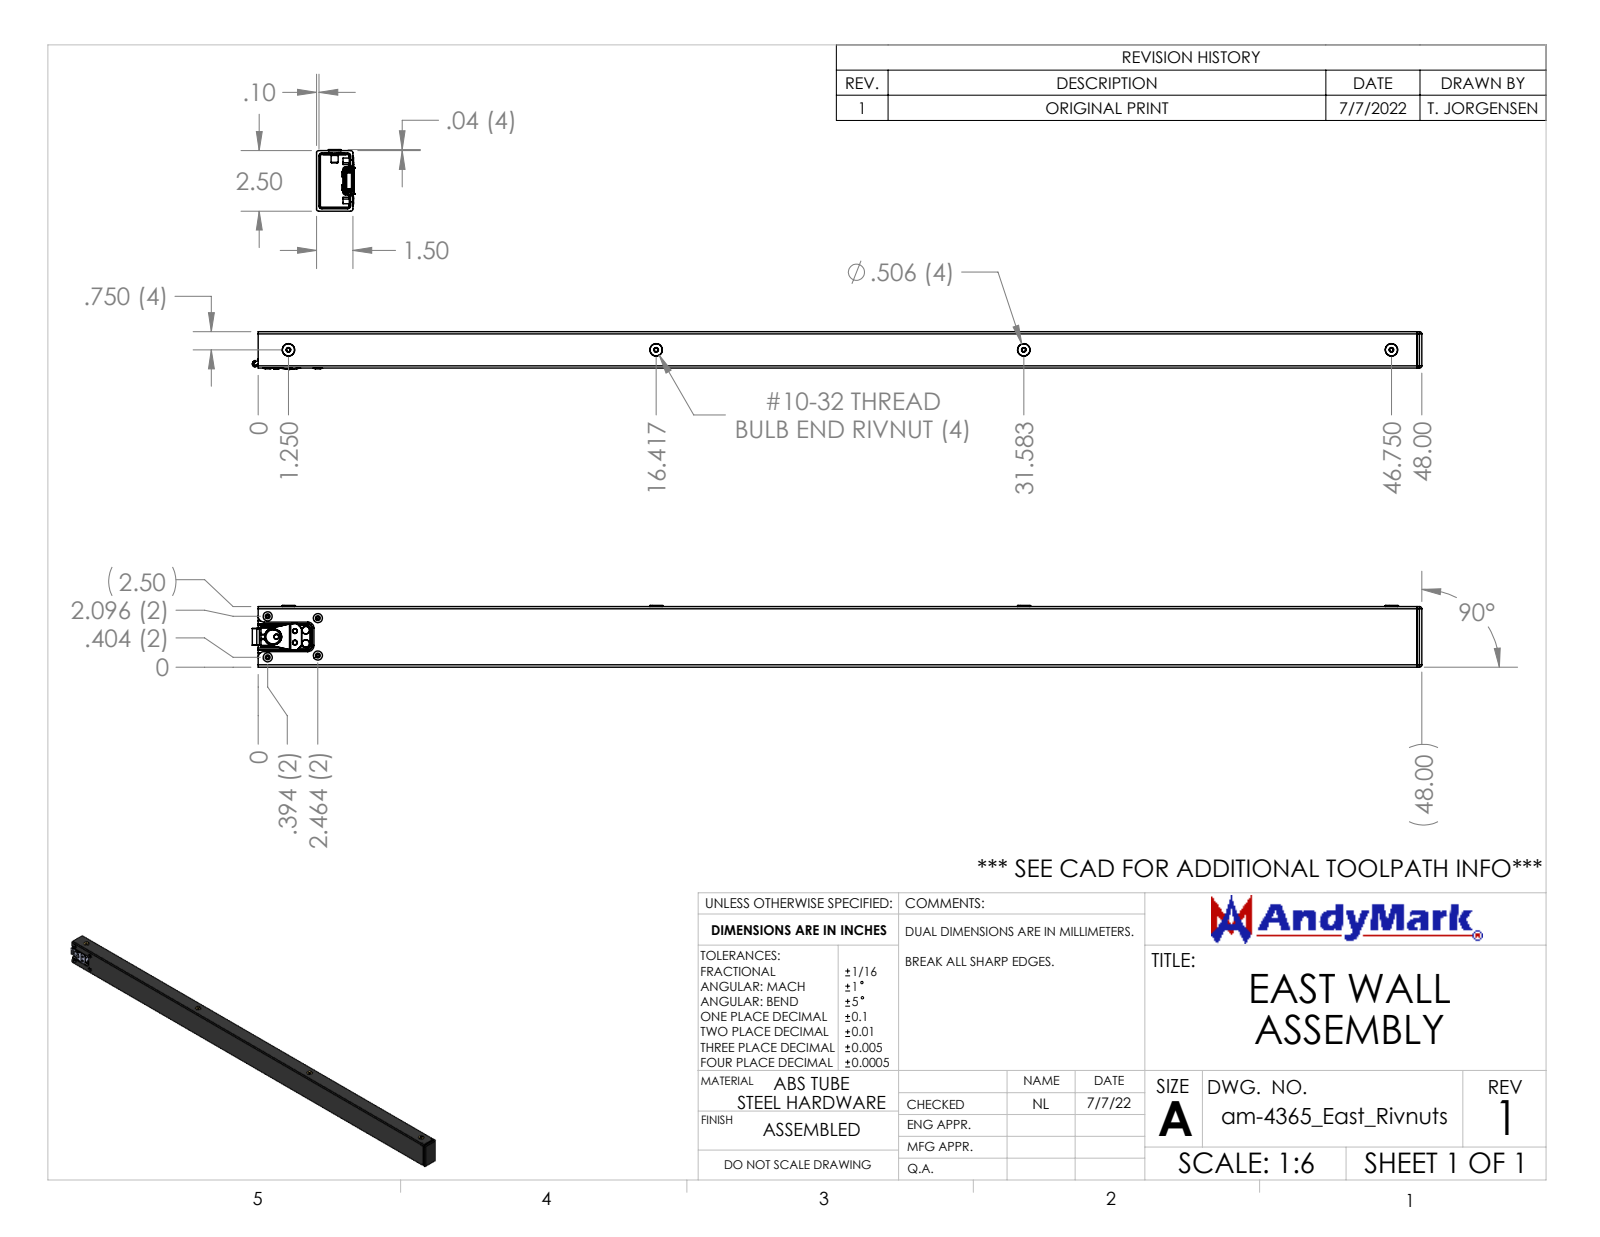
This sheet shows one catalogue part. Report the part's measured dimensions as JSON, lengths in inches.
{"part_name": "L903-7336 v5 v4_9; am-1226 steel rivet 1875 125-250 grip; Tube plug End Cap; am-4365_East_Rivnuts East Wall (+8 more)", "step_written_by": "SolidWorks 2022 (CONFIG_CONTROL_DESIGN)", "units": "inches", "bodies": {"solids": 22, "faces": 1140, "planar": 367, "cylindrical": 427, "other": 346}, "overall_size": [48.24, 2.538, 1.556], "volume_in3": 38.03, "surface_area_in2": 763.2, "round_holes": [[0.1, 4], [0.165, 4], [0.19, 4], [0.201, 4], [0.205, 4], [0.339, 4], [0.189, 2], [0.039, 1], [0.118, 1], [0.122, 1], [0.134, 1], [0.142, 1]], "round_bosses_or_shafts": [[0.51, 4], [0.375, 4], [0.358, 4], [0.296, 4], [0.187, 4], [0.315, 2], [0.213, 2], [0.157, 2]], "partial_cylinders_radius": [[0.004, 42], [0.039, 21], [0.02, 13], [0.094, 8], [0.059, 7], [0.067, 7], [0.071, 7], [0.079, 6]], "face_to_face_distances": [0.1, 1.4, 1.5, 2.4, 1.3, 2.5, 2.3, 0.047, 0.268, 0.065], "hole_center_spacings": [0.024, 0.138, 0.551, 0.552, 0.688, 0.704, 0.85, 0.875]}
